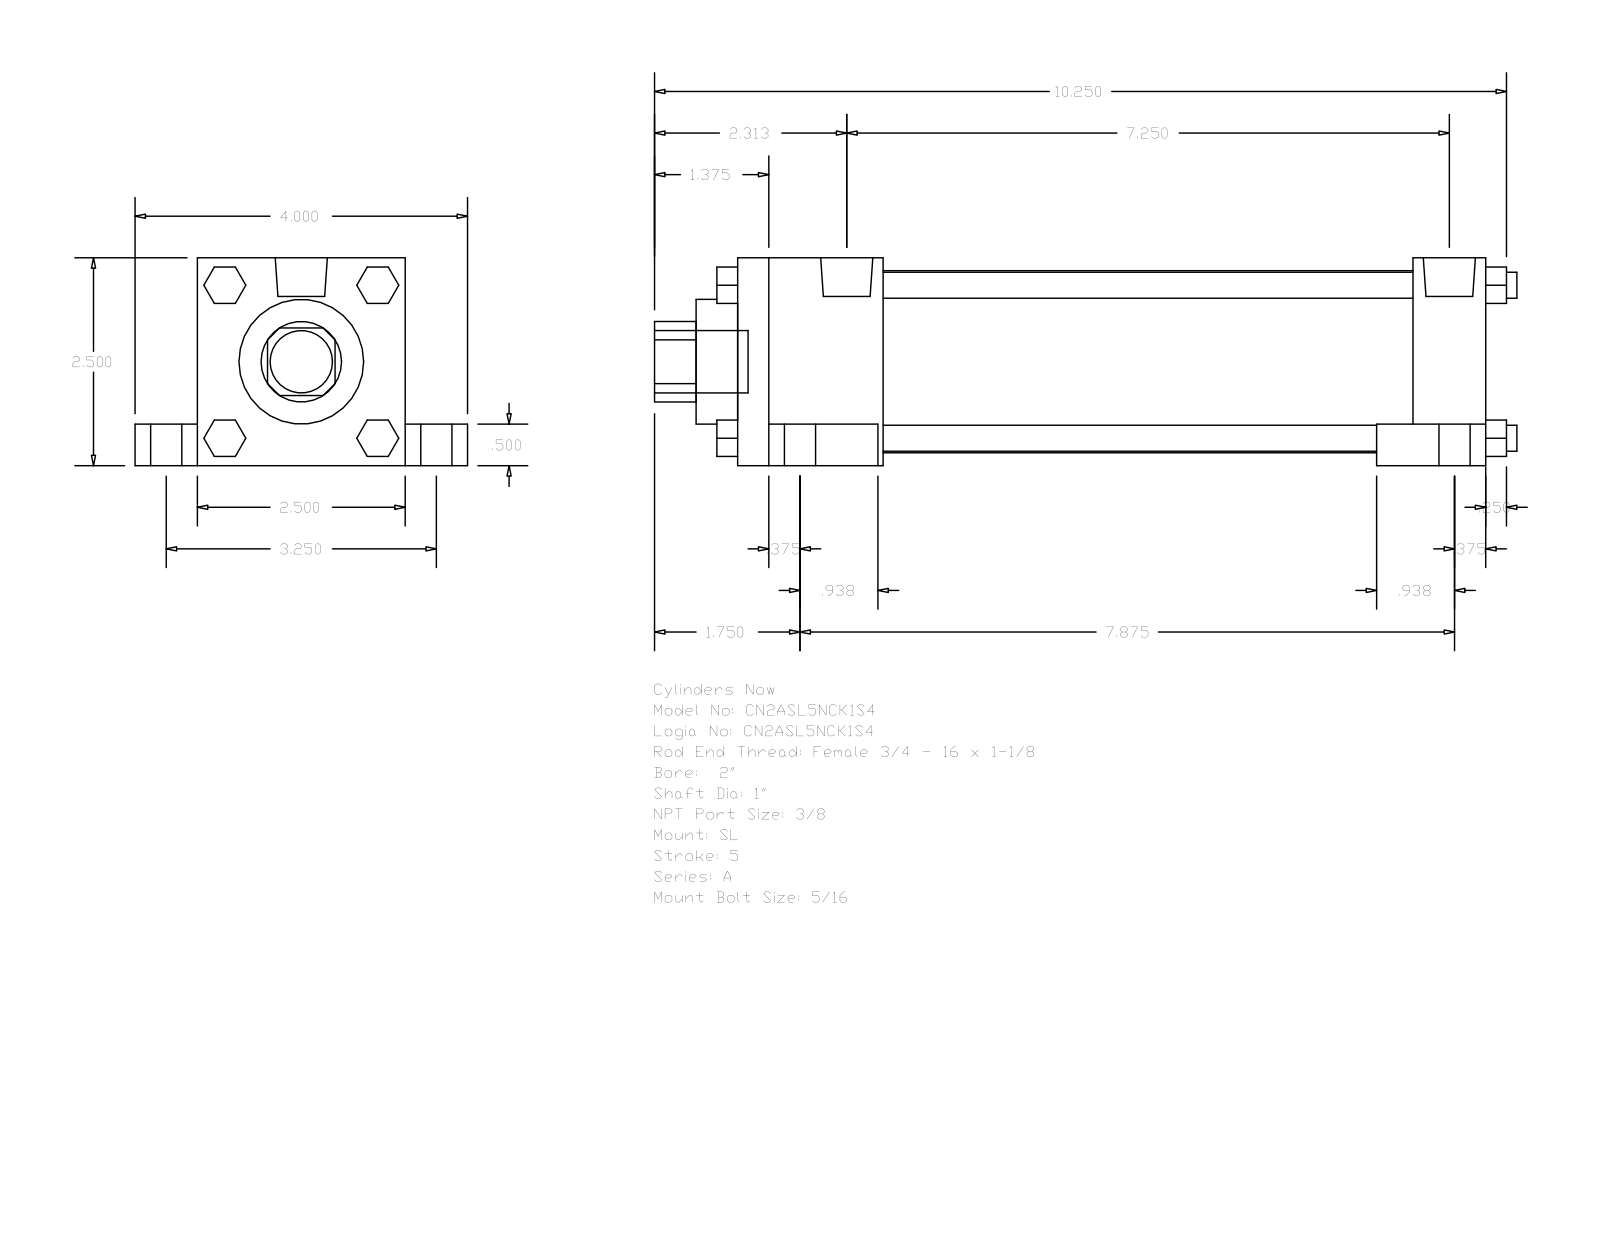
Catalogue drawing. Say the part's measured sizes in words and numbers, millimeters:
The part is named "A_SL__0200_1". Its 3-D file was written by "GSSL Pune (CONFIG_CONTROL_DESIGN)". It is 0 solids with 148 faces: 112 planar, 36 cylindrical and 0 other. Overall it measures 263.52 by 101.6 by 63.5 millimeters. Round holes: 1 of diameter 25.4, 1 of diameter 38.1, 1 of diameter 55.63. Round bosses or shafts: 4 of diameter 15.88, 4 of diameter 9.53, 4 of diameter 7.94, 4 of diameter 5.56, 2 of diameter 15.93, 1 of diameter 19.05. Partial cylindrical surfaces (rounded edges, fillets, slot ends): 1 of radius 12.29. The main face-to-face distances are 63.5, 228.6, 12.7, 50.8, 22.22, 19.05, 82.55, 9.52, 44.45, 184.15.
